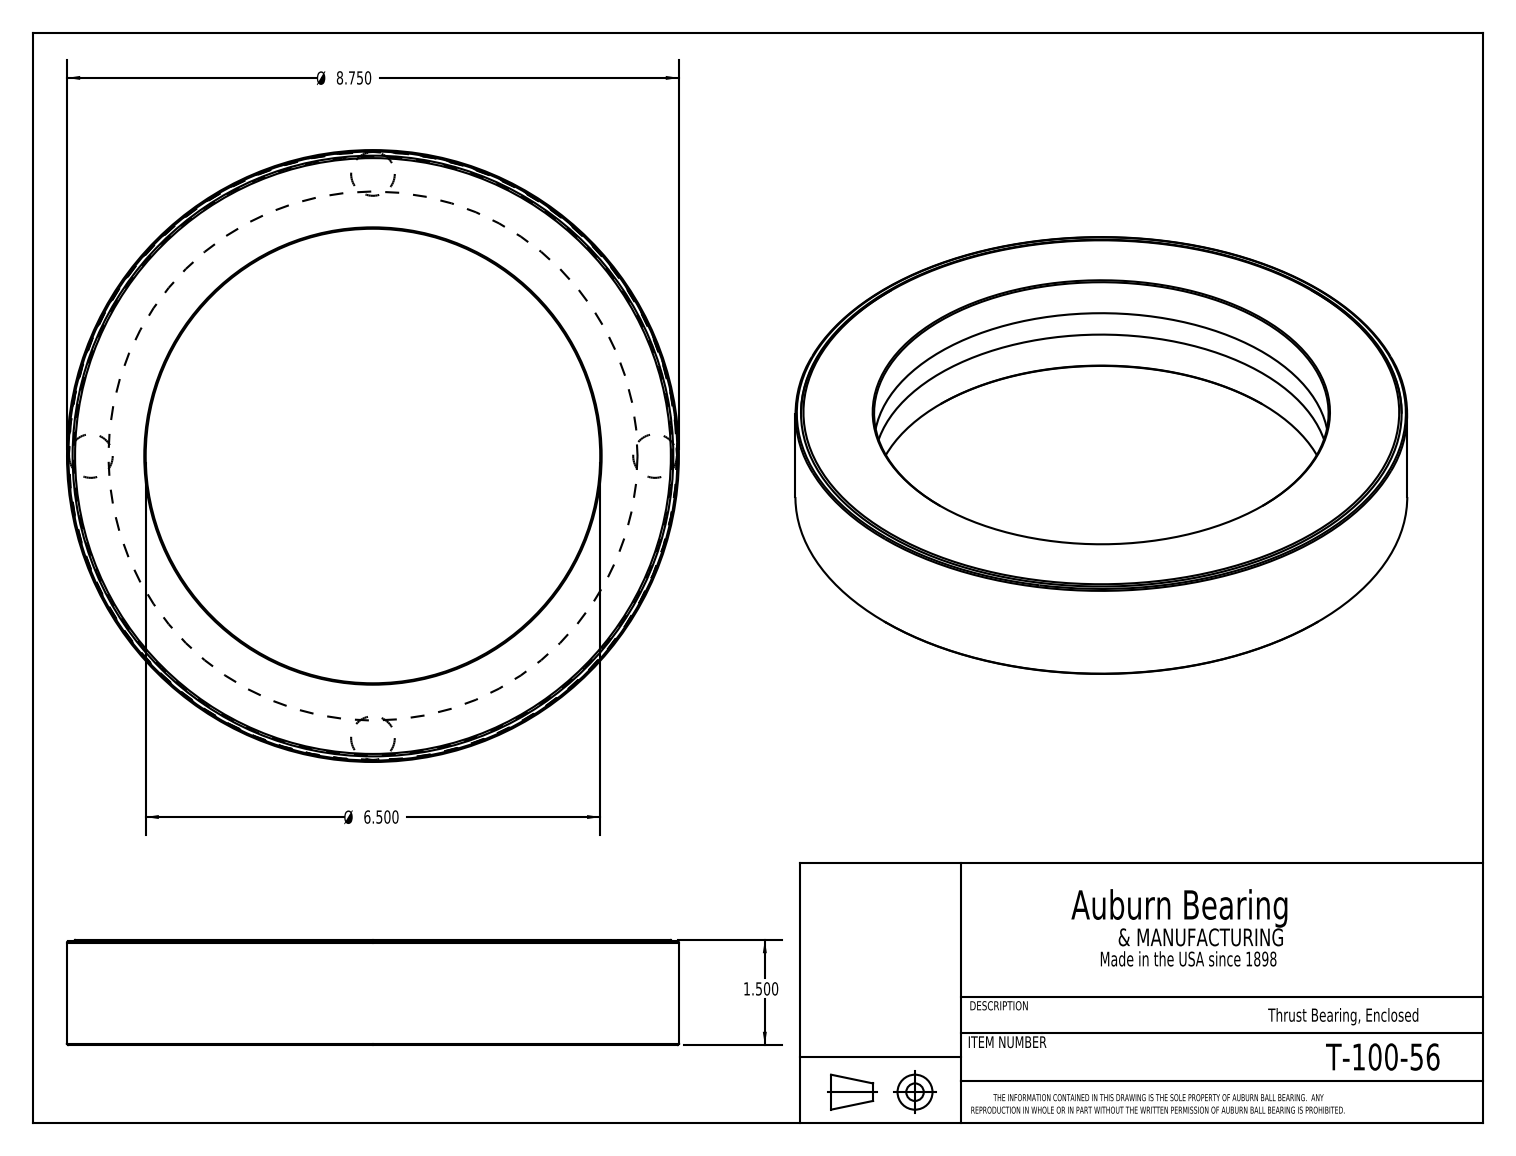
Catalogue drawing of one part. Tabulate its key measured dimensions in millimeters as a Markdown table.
| quantity | value |
| --- | --- |
| part name | T-100-56 |
| STEP written by | SolidWorks 2016 (CONFIG_CONTROL_DESIGN) |
| units | millimeters |
| bodies | 6 solids, 28 faces (9 planar, 7 cylindrical, 12 other) |
| overall size | 222.3 × 222.3 × 38.1 |
| volume | 469 000 mm³ |
| surface area | 142 400 mm² |
| round holes (diameter × count) | 165.1 × 1, 218.2 × 1, 221.2 × 1 |
| round bosses / shafts (diameter × count) | 222.3 × 1, 220.9 × 1 |
| main face-to-face distances | 14.3, 23.8, 38.1, 9.5, 37.7, 23.4, 13.9, 0.4, 37.2, 22.9 |
